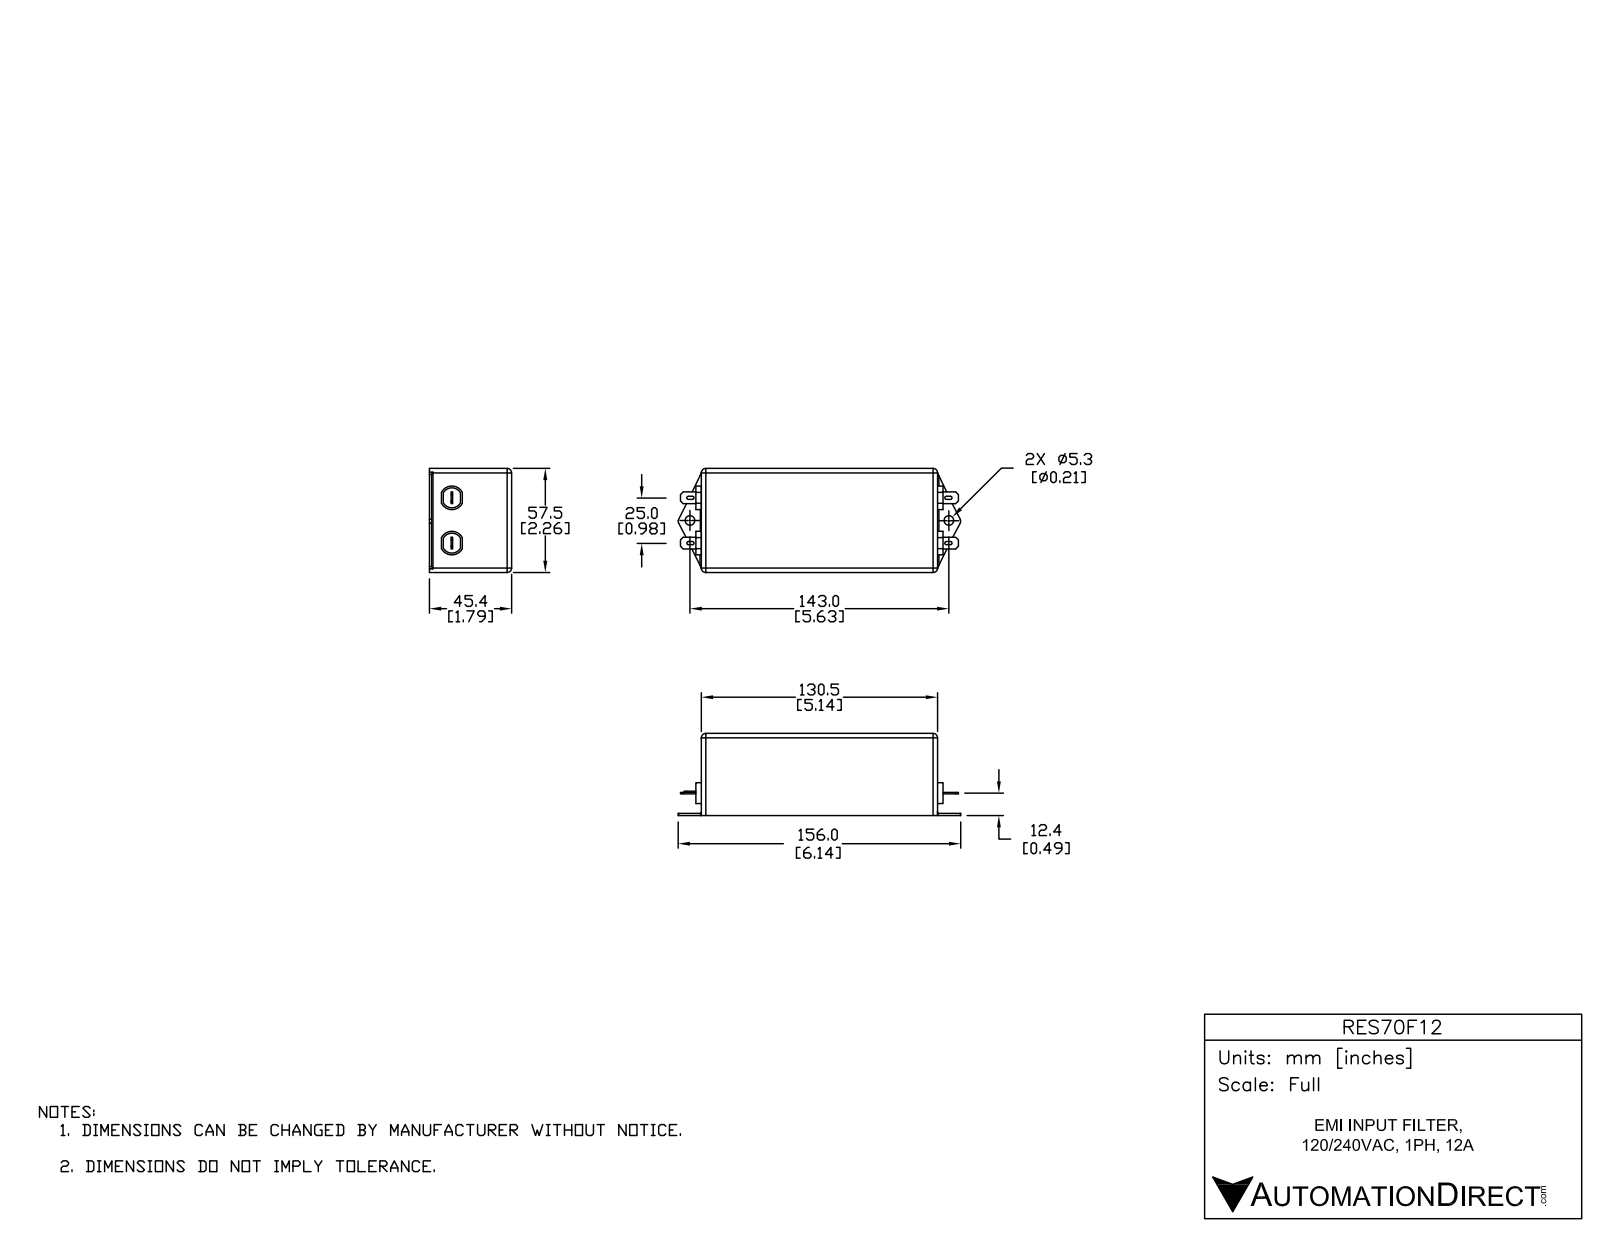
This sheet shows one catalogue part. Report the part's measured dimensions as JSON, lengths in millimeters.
{"part_name": "RES70F12", "step_written_by": "SolidWorks 2015 (AUTOMOTIVE_DESIGN)", "units": "millimeters", "bodies": {"solids": 1, "faces": 133, "planar": 79, "cylindrical": 50, "other": 4}, "overall_size": [155.44, 57.5, 45.4], "volume_mm3": 341903, "surface_area_mm2": 34102, "round_holes": [[5.3, 2], [2, 1]], "partial_cylinders_radius": [[2.5, 10], [0.88, 8], [0.75, 2], [5.5, 2], [6.5, 2]], "face_to_face_distances": [45.4, 57.5, 130.5, 1.2, 44.2, 1.5, 132, 133.5, 0.8, 12], "hole_center_spacings": [143]}
